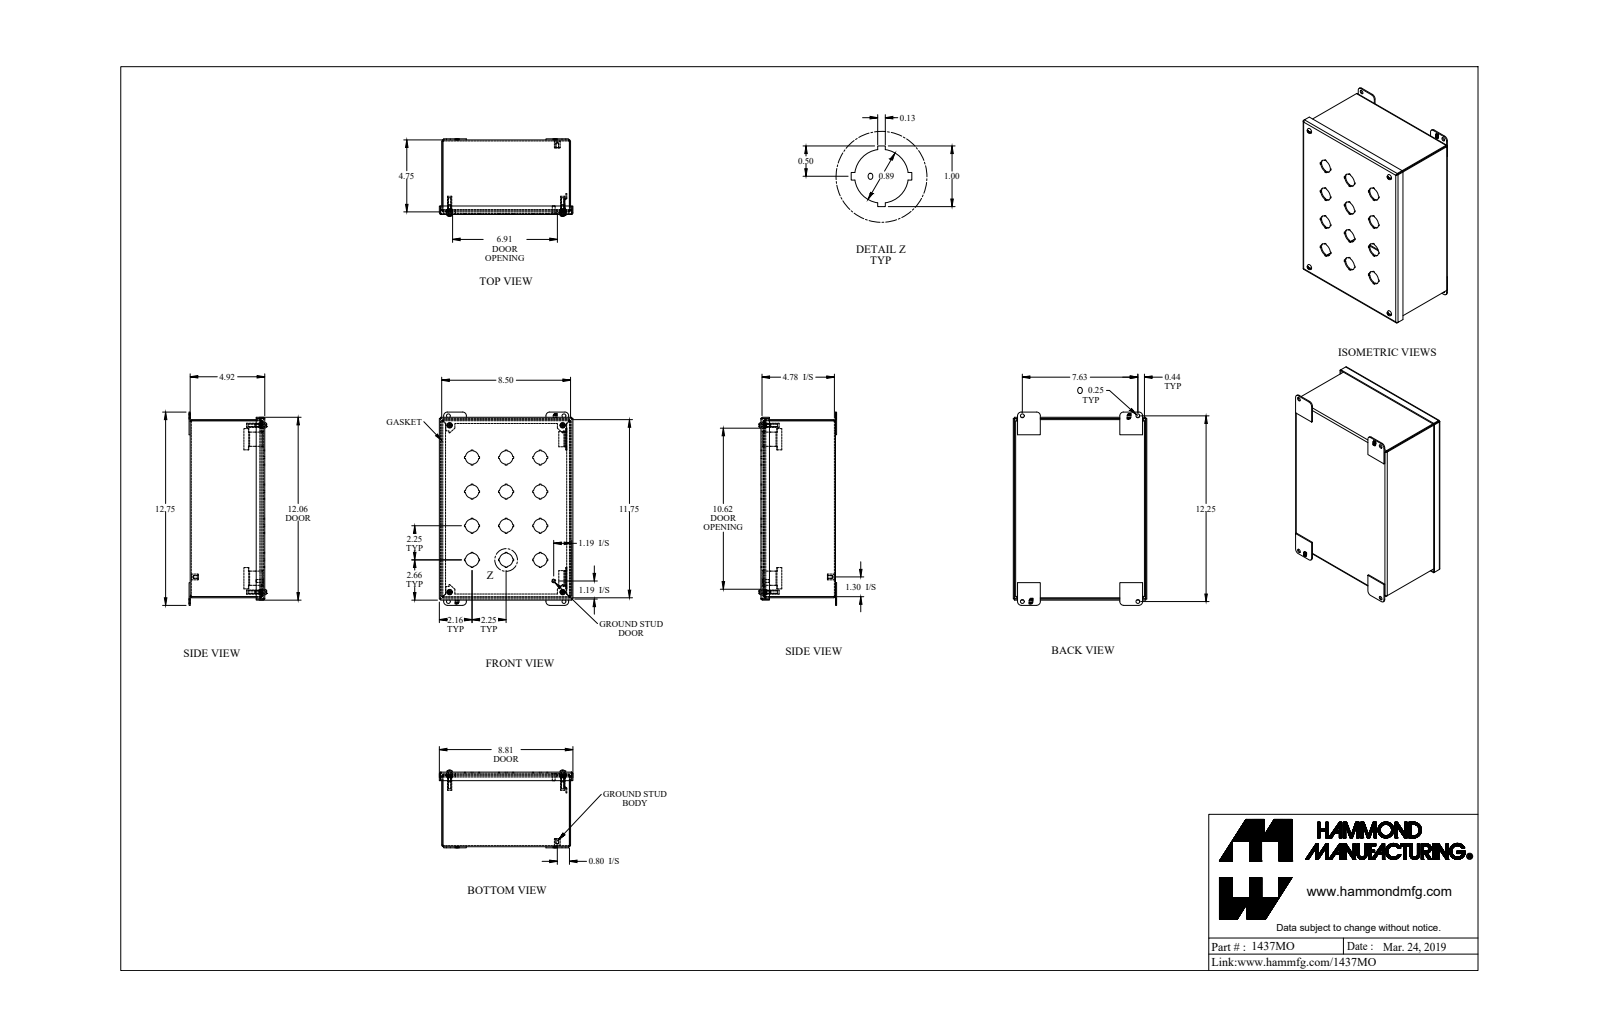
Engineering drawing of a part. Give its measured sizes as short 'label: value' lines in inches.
name: 1437MO_Default
written by: SolidWorks 2019 (CONFIG_CONTROL_DESIGN)
unit: in
bodies: 23 solids, 907 faces (643 planar, 208 cylindrical, 56 other)
size: 12.75 × 8.812 × 5.121
volume: 34.47 in³; area: 921.7 in²
holes: 12× ⌀0.886, 8× ⌀0.25, 4× ⌀0.159, 4× ⌀0.406, 1× ⌀0.156
bosses: 4× ⌀0.39, 4× ⌀0.275, 4× ⌀0.19, 4× ⌀0.148, 1× ⌀0.375, 1× ⌀0.25, 1× ⌀0.188
rounds: 12× R0.036, 12× R0.108, 8× R0.25, 4× R0.029, 4× R0.086, 4× R0.16, 4× R0.171
face distances: 0.072, 4.85, 8.428, 4.922, 4.778, 0.072, 11.678, 8.356, 8.5, 11.75
hole spacings: 2.25, 5.031, 3.182, 4.5, 11, 11.626, 4.619, 0.63
